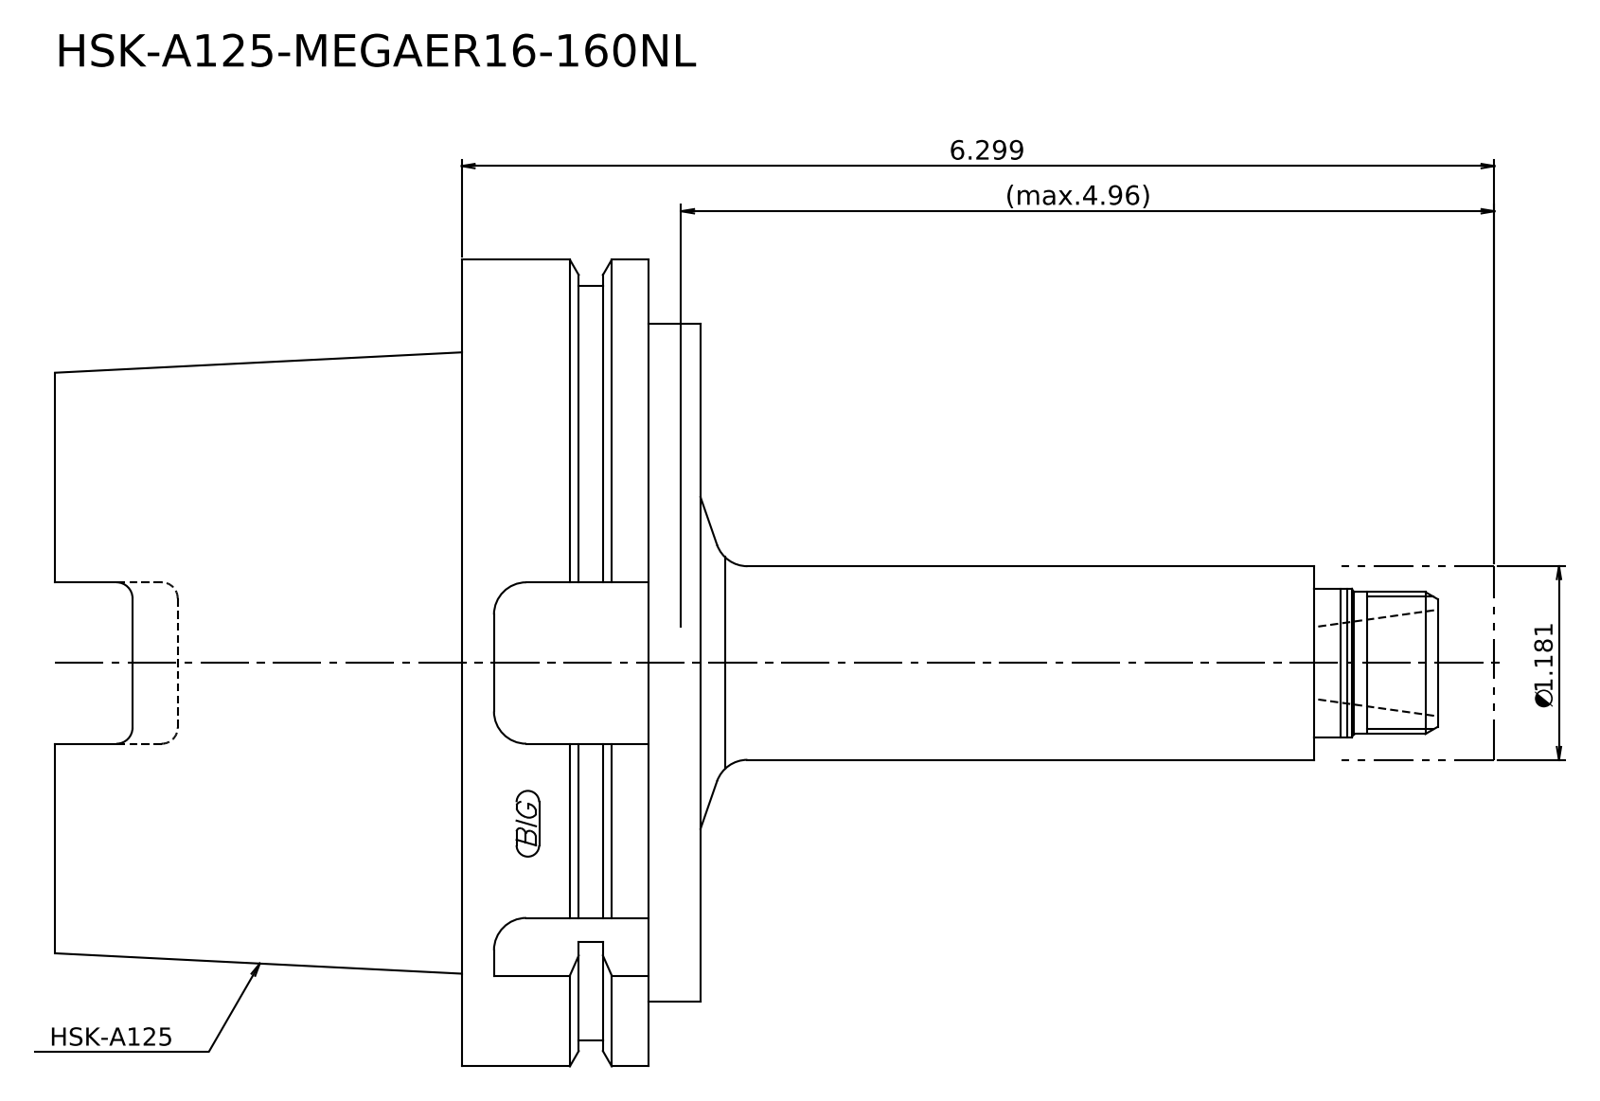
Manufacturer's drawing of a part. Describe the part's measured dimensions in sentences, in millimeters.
Its 3-D file was written by "Kubotek KeyCreator 2011 V10.0.2 (22737) (automotive_design)". It is 2 solids with 24 faces: 10 planar, 8 cylindrical and 6 other. Overall it measures 223 by 125 by 125 millimeters. Its volume is 944 168 cubic millimeters and its surface area 71 844 square millimeters. Round bosses or shafts: 1 of diameter 125, 1 of diameter 117, 1 of diameter 105, 1 of diameter 30, 1 of diameter 23, 1 of diameter 22. The main face-to-face distances are 100, 37, 63, 8, 29, 92, 98, 106, 135, 198.
